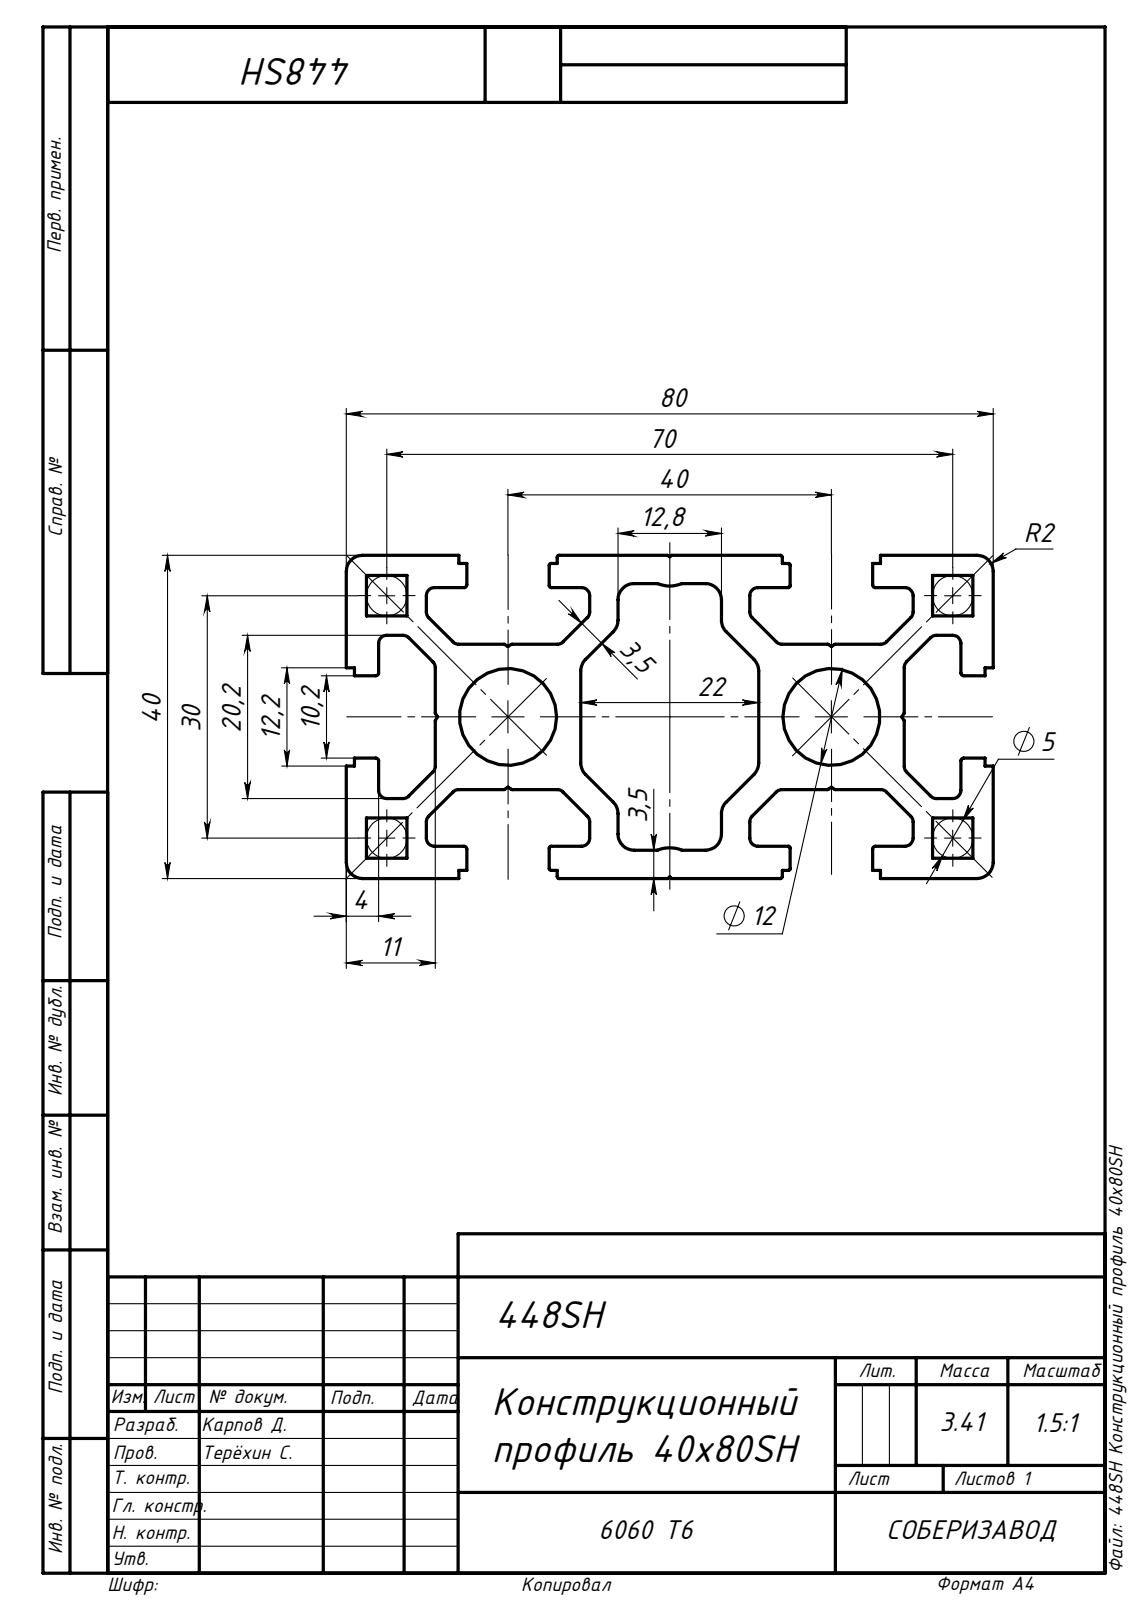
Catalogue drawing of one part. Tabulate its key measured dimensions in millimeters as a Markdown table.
| quantity | value |
| --- | --- |
| STEP written by | SolidWorks 2019 (AUTOMOTIVE_DESIGN) |
| units | millimeters |
| bodies | 1 solid, 226 faces (144 planar, 82 cylindrical, 0 other) |
| overall size | 1000 × 80 × 40 |
| volume | 1 264 000 mm³ |
| surface area | 709 300 mm² |
| round holes (diameter × count) | 12 × 2 |
| partial cylindrical surfaces (radius × count) | 1 × 36, 0.25 × 16, 2 × 16, 0.35 × 8, 4 × 2 |
| main face-to-face distances | 3.5, 40, 29, 11, 5, 4, 25, 7.5, 8.5, 2.5 |
| hole center spacings | 40 |
